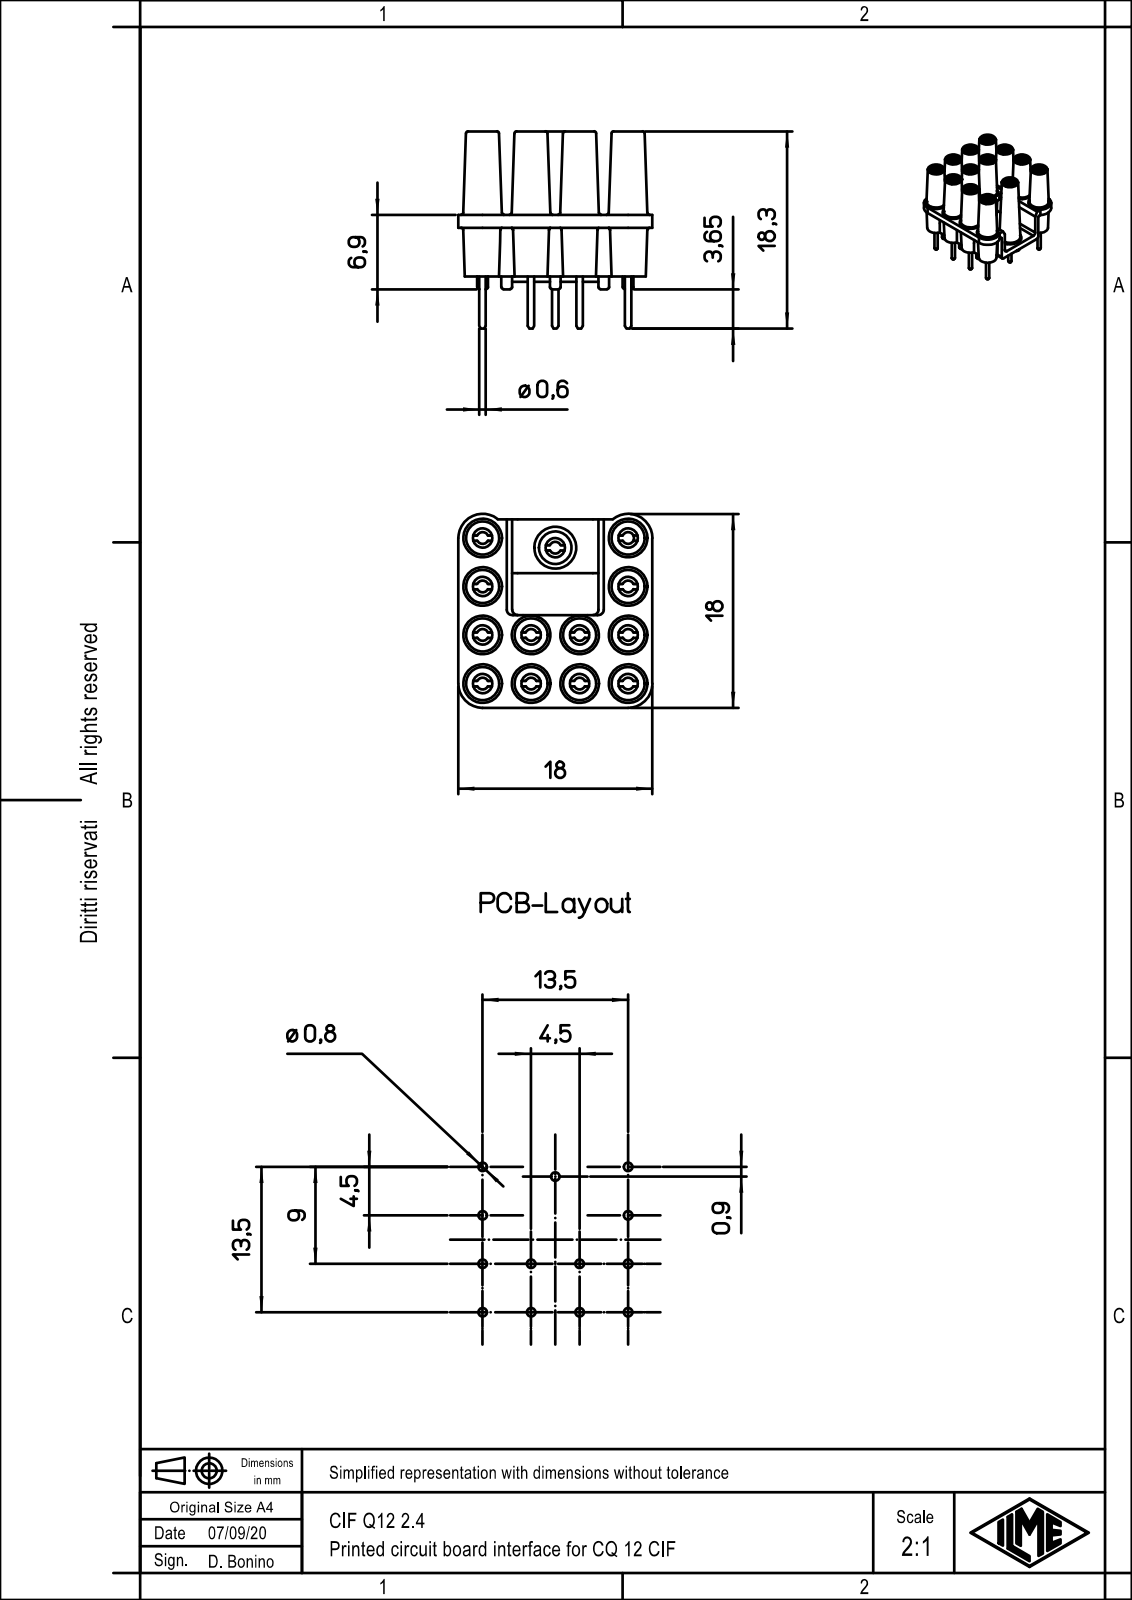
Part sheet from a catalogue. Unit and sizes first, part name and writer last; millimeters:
Units: millimetres
Overall size (bounding box): 18.3 × 18 × 18
Round holes (diameter × count): ⌀2 ×13
Round bosses / shafts (diameter × count): ⌀0.6 ×13, ⌀1 ×10, ⌀3.6 ×2
Partial cylindrical surfaces — rounded edges, fillets, slot ends (radius × count): R0.55 ×13, R1.8 ×10, R0.5 ×8, R2.25 ×4
Main face-to-face distances: 4.5, 1.2, 5, 5.7, 0.5, 13.45, 13.5, 7.75, 2.85, 1.65
Hole centre spacings: 4.5, 10.06, 6.36, 9, 14.23, 13.5, 16.22, 12.73
Volume: 1 815 mm³ · Surface area: 2 977 mm²
Bodies: 1 solid, 403 faces (171 planar, 134 cylindrical, 98 other)
Part name (STEP PRODUCT): CIF_Q12_2.4
STEP written by: Creo Elements/Direct Modeling 20.1B 02-Apr-2019 (C) Parametric Technology GmbH (AUTOMOTIVE_DESIGN)
